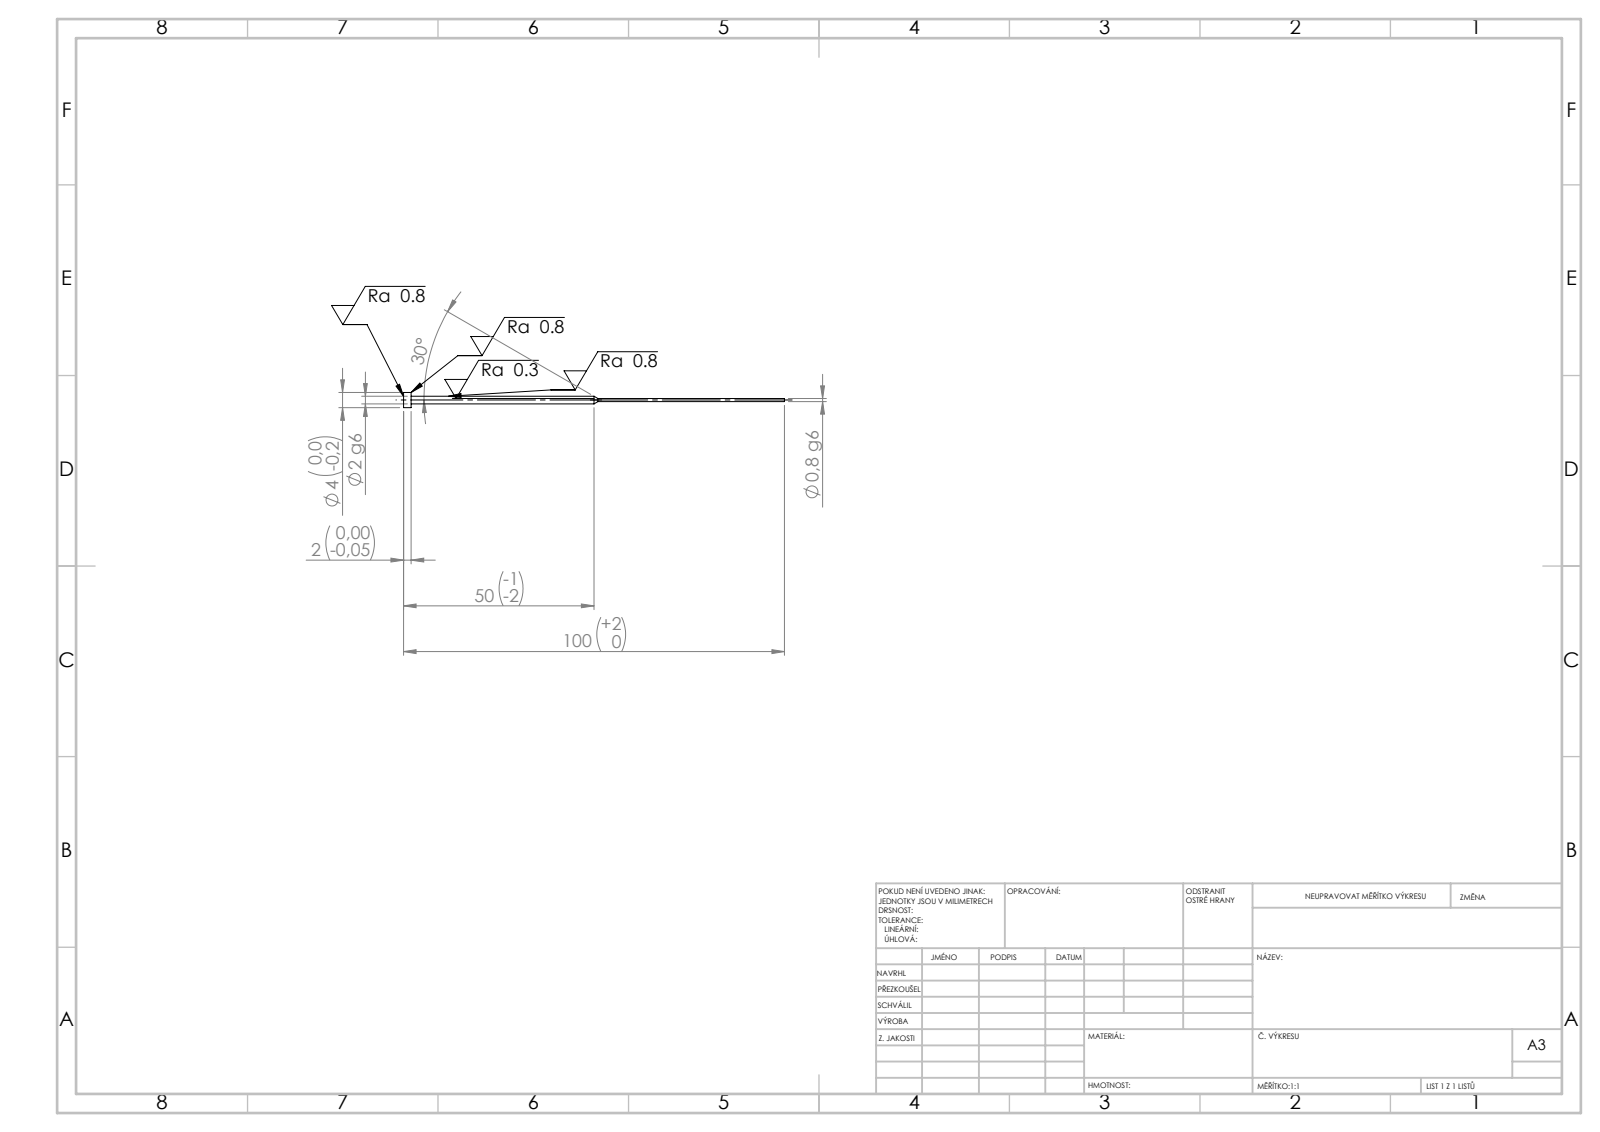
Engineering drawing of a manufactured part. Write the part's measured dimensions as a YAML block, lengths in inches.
step_written_by: "SolidWorks 2019 (CONFIG_CONTROL_DESIGN)"
units: inches
bodies: {solids: 1, faces: 11, planar: 3, cylindrical: 6, other: 2}
overall_size: [3.937, 0.157, 0.157]
volume: 0.012
surface_area: 0.741
round_bosses_or_shafts:
  - {diameter: 0.157, count: 1}
  - {diameter: 0.079, count: 1}
  - {diameter: 0.031, count: 1}
face_to_face_distances: [0.079, 3.858, 3.937]
